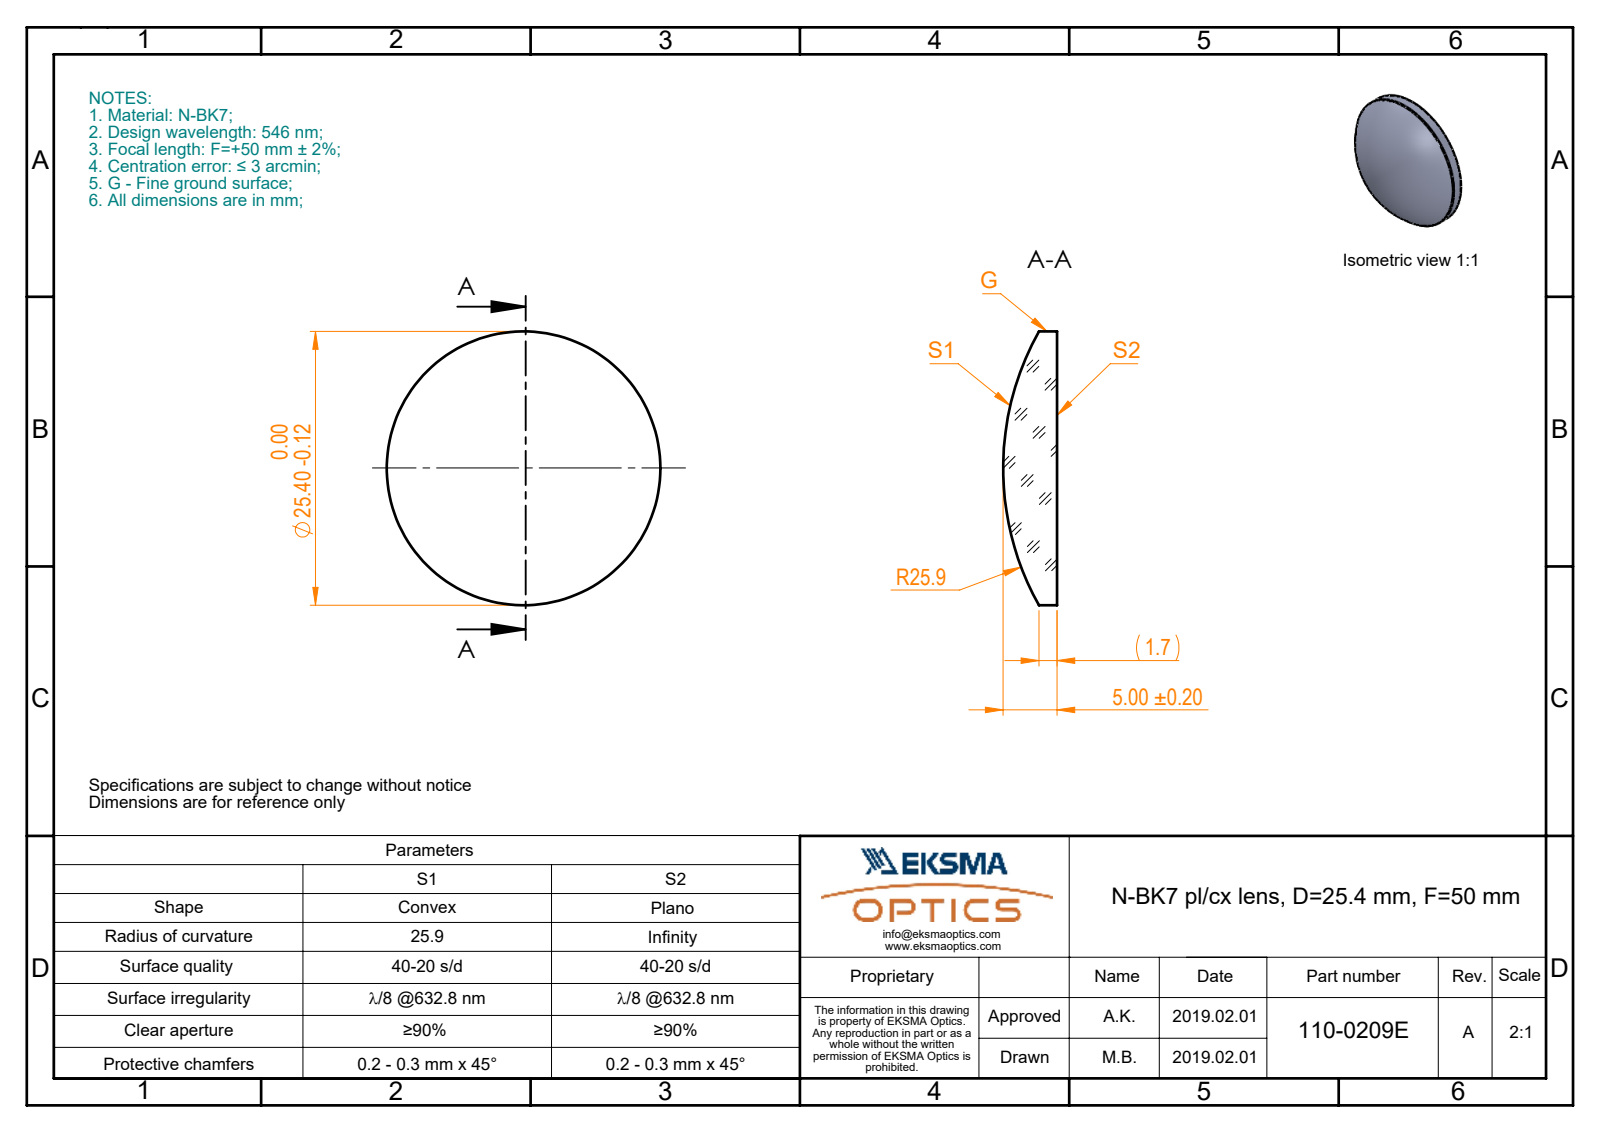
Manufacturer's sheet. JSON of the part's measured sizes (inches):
{"part_name": "110-0209E BK7 pl-cx 25.4 F50", "step_written_by": "SolidWorks 2017 (CONFIG_CONTROL_DESIGN)", "units": "inches", "bodies": {"solids": 1, "faces": 5, "planar": 1, "cylindrical": 2, "other": 2}, "overall_size": [1, 1, 0.197], "volume_in3": 0.104, "surface_area_in2": 1.832, "round_bosses_or_shafts": [[1, 1]]}
